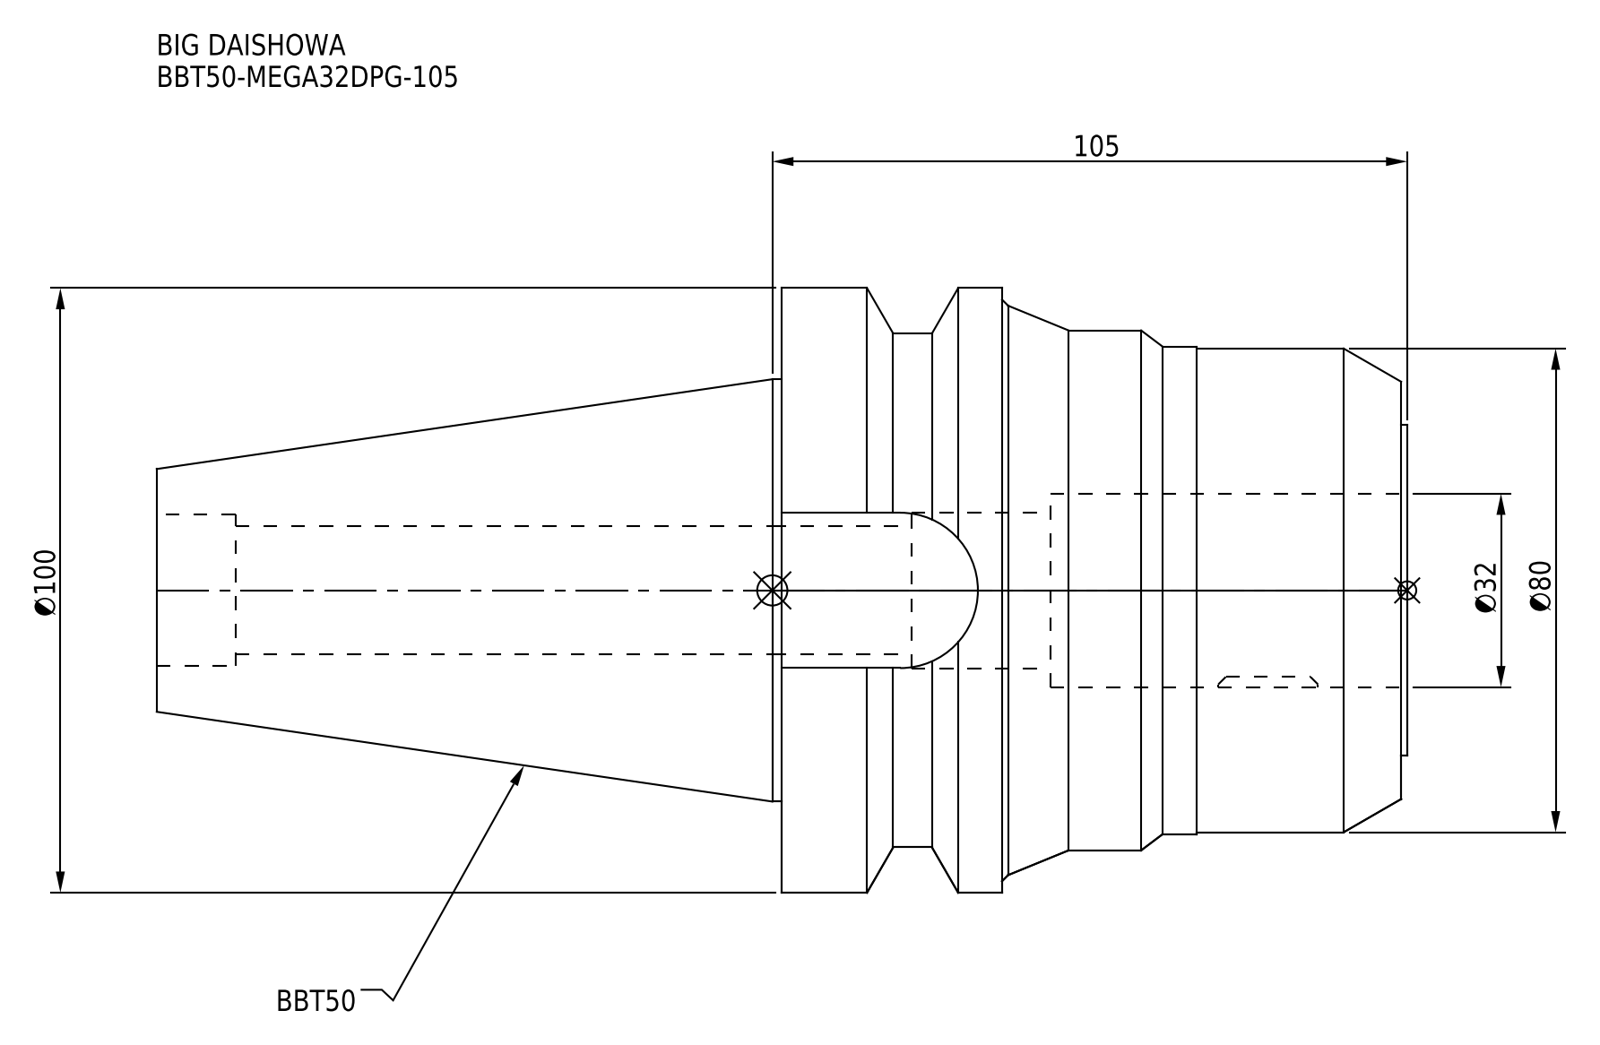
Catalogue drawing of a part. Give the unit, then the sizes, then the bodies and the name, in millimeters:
Units: millimetres
Overall size (bounding box): 206.8 × 100 × 100
Round holes (diameter × count): ⌀21.2 ×1, ⌀25 ×1, ⌀25.8 ×1, ⌀32 ×1
Round bosses / shafts (diameter × count): ⌀100 ×1, ⌀86 ×1, ⌀85 ×1, ⌀80.7 ×1, ⌀80 ×1, ⌀69.85 ×1, ⌀54.7 ×1
Partial cylindrical surfaces — rounded edges, fillets, slot ends (radius × count): R12.85 ×1
Main face-to-face distances: 103.5, 1, 102.5, 206.8, 205.8, 103.3, 70.8, 67, 66, 36.5
Volume: 748 534 mm³ · Surface area: 75 641 mm²
Bodies: 1 solid, 57 faces (15 planar, 28 cylindrical, 14 other)
Part name (STEP PRODUCT): BBT50-MEGA32DPG-105
STEP written by: CREO PARAMETRIC BY PTC INC, 2016380 (AUTOMOTIVE_DESIGN)
